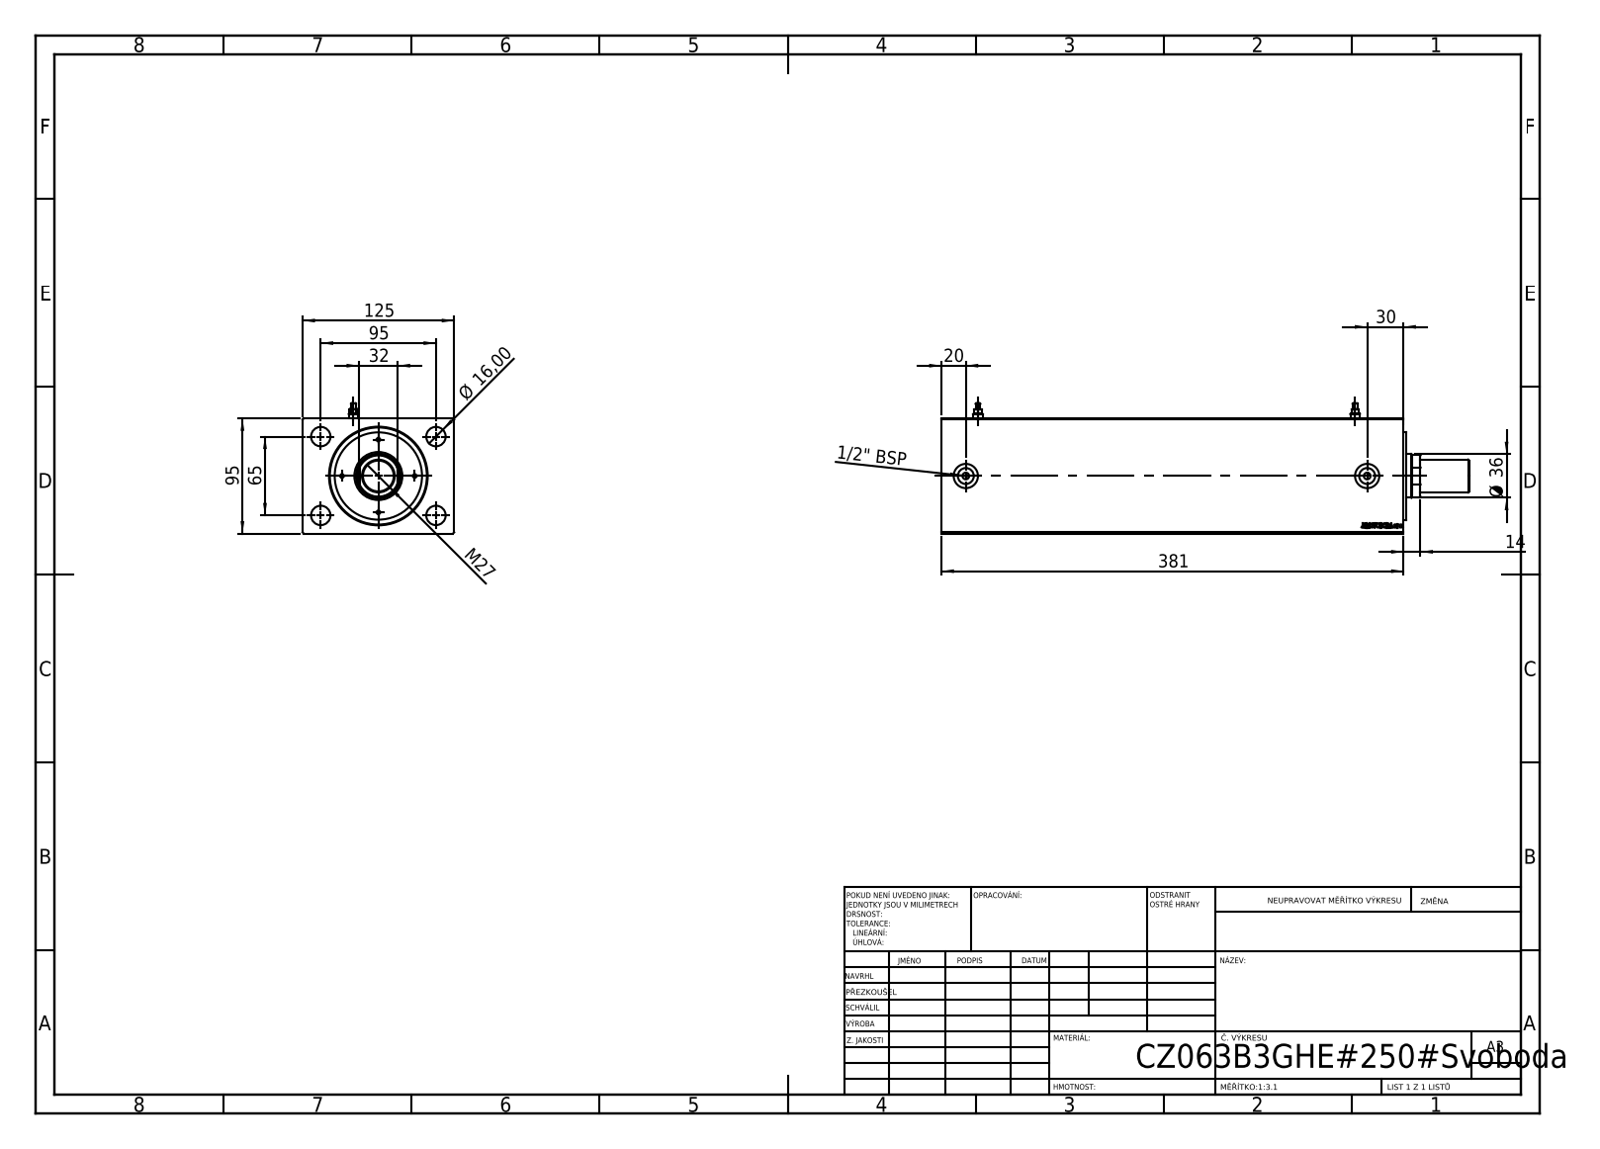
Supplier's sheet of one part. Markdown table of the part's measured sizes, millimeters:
| quantity | value |
| --- | --- |
| part name | Zatka_Cushioning3; V500CZ; V500CZ_SMALL_MALE_METRIC; V500CZ_B_VC |
| STEP written by | SolidWorks 2019 (CONFIG_CONTROL_DESIGN) |
| units | millimeters |
| bodies | 6 solids, 940 faces (426 planar, 76 cylindrical, 438 other) |
| overall size | 435 × 125 × 107.5 |
| volume | 3 964 000 mm³ |
| surface area | 352 464 mm² |
| round holes (diameter × count) | 3 × 4, 16 × 4, 1.8 × 2, 5.5 × 2, 8 × 2, 13.16 × 2, 20 × 2, 25.5 × 1, 36 × 1, 37 × 1, 63 × 1, 80 × 1 |
| round bosses / shafts (diameter × count) | 7.8 × 2, 3.8 × 2, 72 × 1, 27 × 1 |
| partial cylindrical surfaces (radius × count) | 17.5 × 1 |
| main face-to-face distances | 95, 125, 381, 360.2, 20.8, 14, 12.2, 1.8, 348, 368.8 |
| hole center spacings | 30, 36.91, 42.43, 47.57, 57.55, 78.5, 84.04, 60 |
